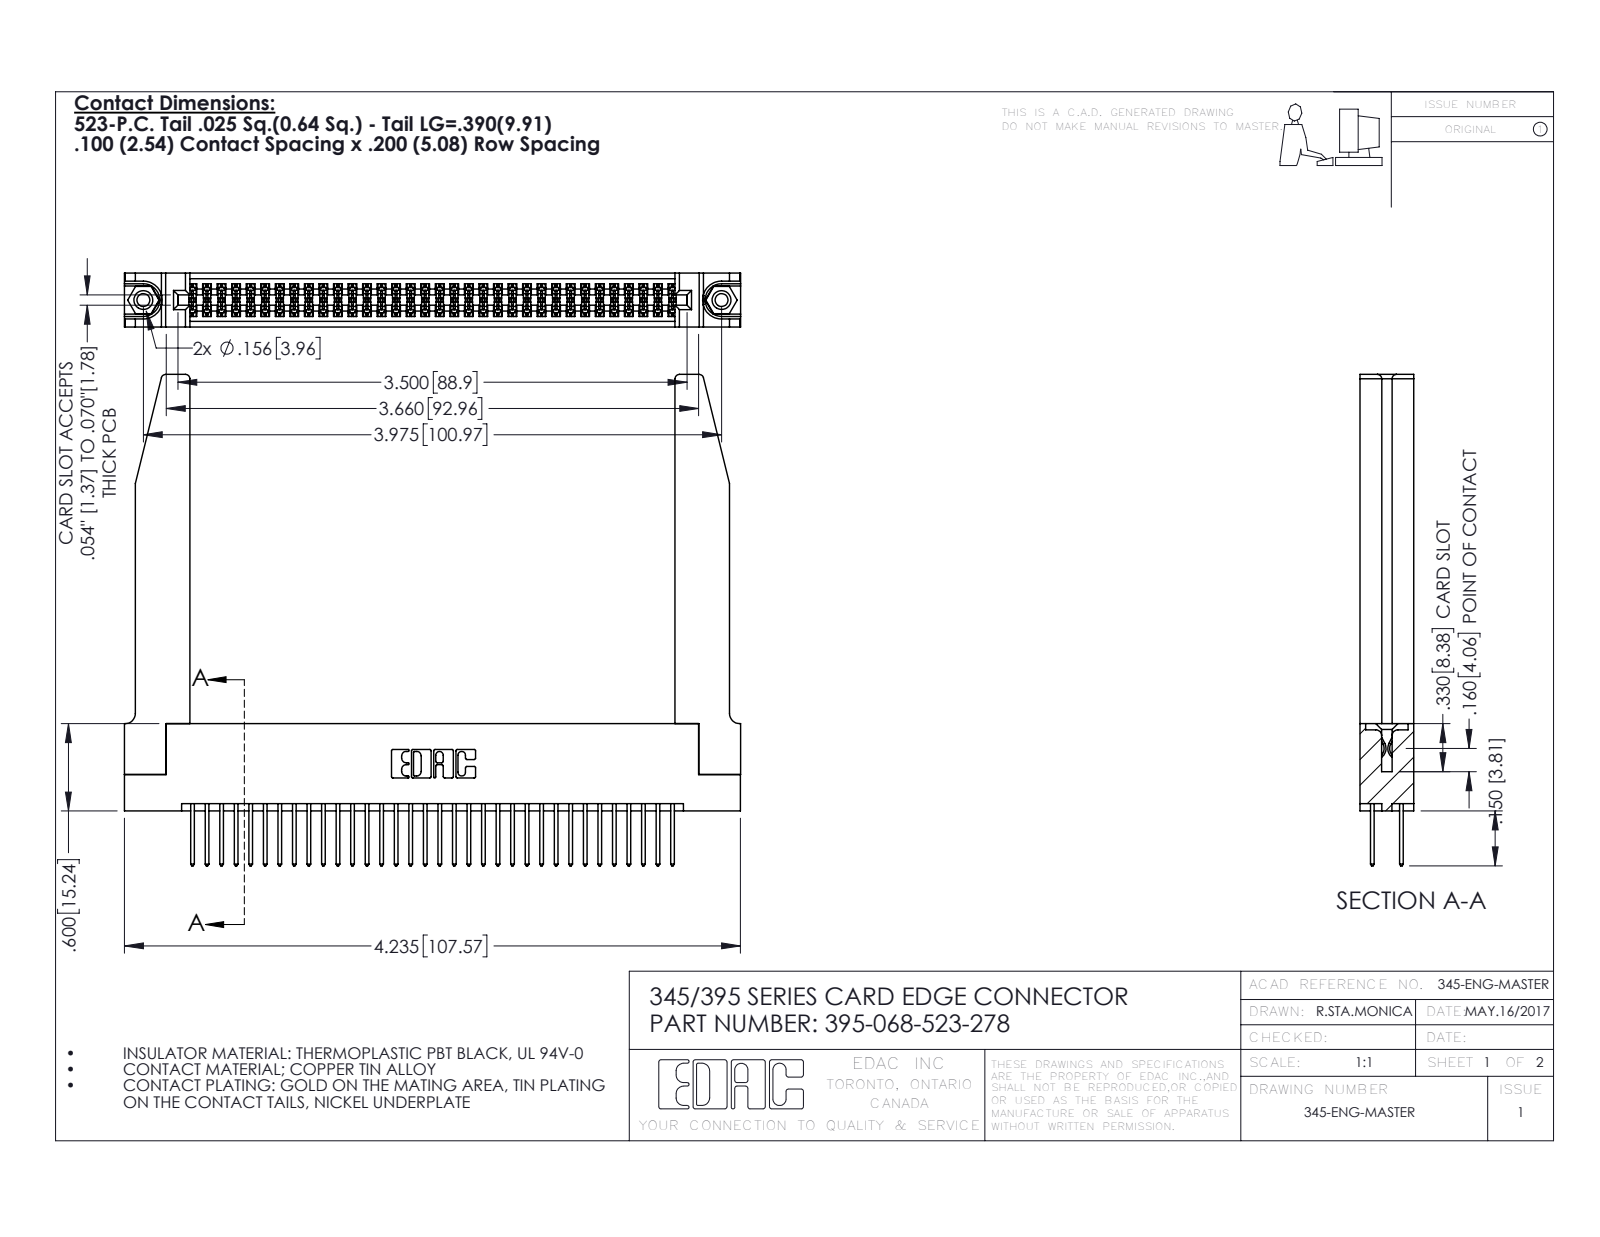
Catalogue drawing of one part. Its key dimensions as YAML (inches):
part_name: "345-292-001_345-293-123; 345 Part_Flush Mounting Lugs - 0.156 Dia-TH; 345-250-001_345-250-001-102; 395-068-523-278 (+1 more)"
step_written_by: "SolidWorks 2016 (CONFIG_CONTROL_DESIGN)"
units: inches
bodies: {solids: 73, faces: 3760, planar: 2466, cylindrical: 1242, other: 52}
overall_size: [4.236, 3.377, 0.37]
volume: 1.116
surface_area: 35.42
round_holes:
  - {diameter: 0.089, count: 2}
  - {diameter: 0.125, count: 2}
  - {diameter: 0.156, count: 2}
  - {diameter: 0.064, count: 1}
round_bosses_or_shafts:
  - {diameter: 0.155, count: 2}
partial_cylinders:
  - {radius: 0.006, count: 102}
  - {radius: 0.01, count: 68}
  - {radius: 0.01, count: 22}
  - {radius: 0.03, count: 8}
  - {radius: 0.007, count: 6}
  - {radius: 0.031, count: 6}
  - {radius: 0.026, count: 3}
  - {radius: 0.014, count: 2}
face_to_face_distances: [0.072, 0.37, 0.298, 0.2, 0.098, 0.272, 0.025, 0.225, 0.175, 0.15]
hole_center_spacings: [0.27, 3.74, 3.975]
